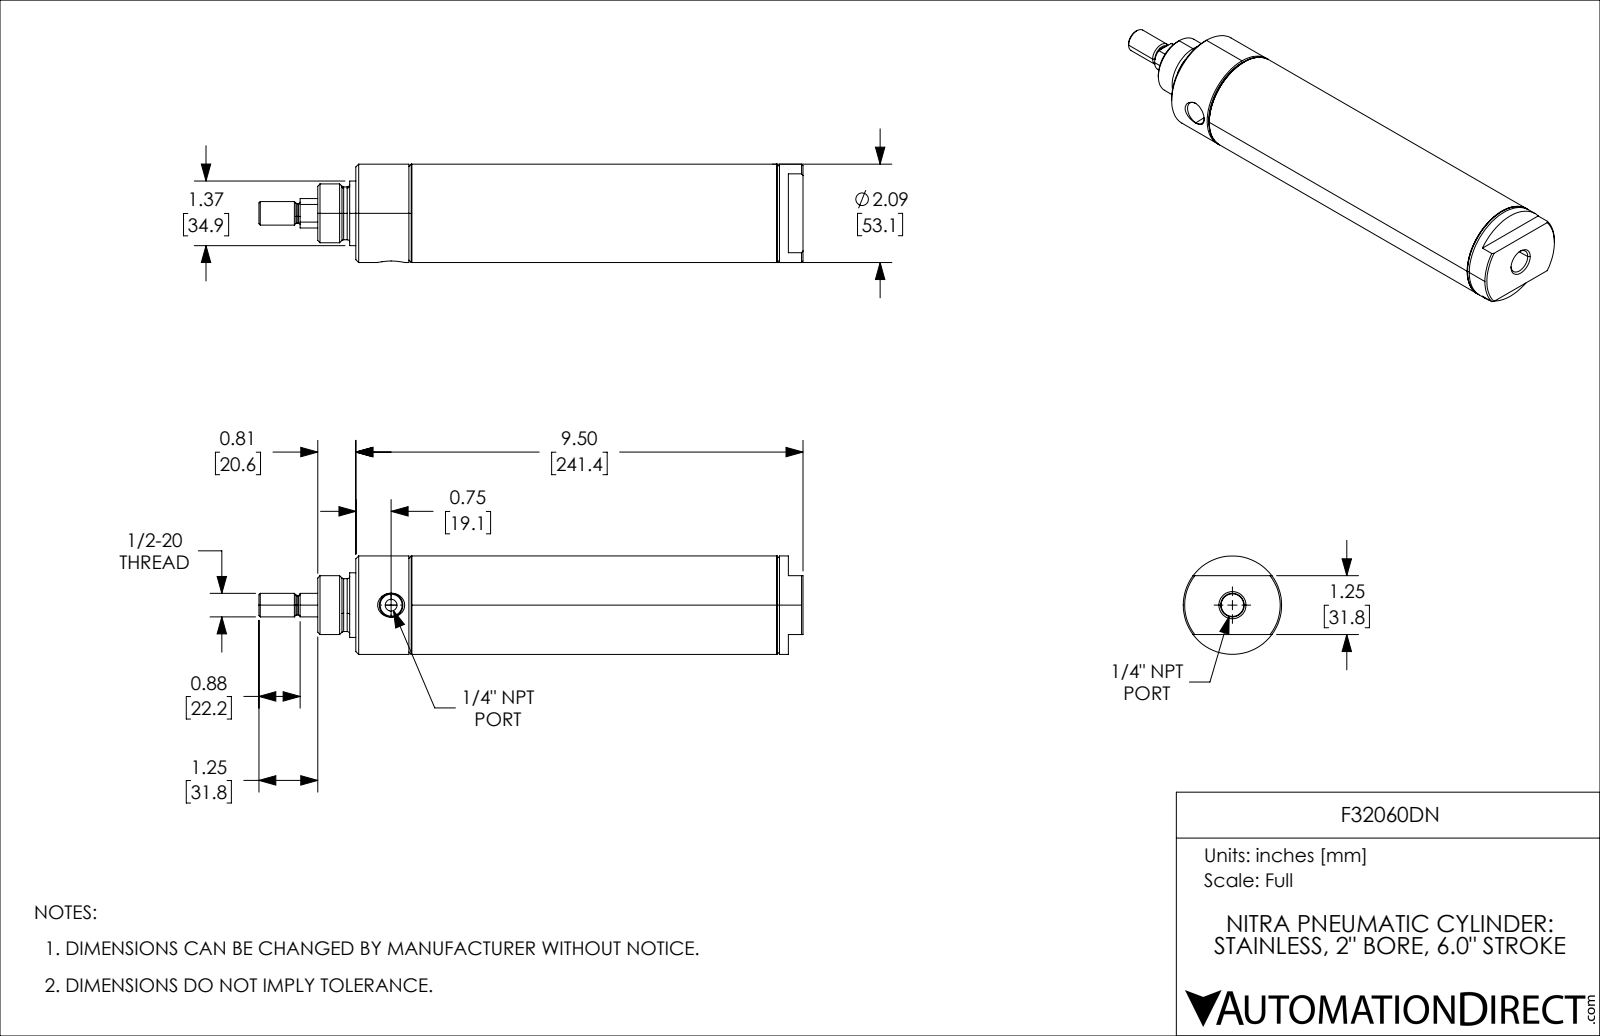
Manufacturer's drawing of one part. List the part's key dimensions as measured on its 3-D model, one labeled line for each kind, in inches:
Part name (STEP PRODUCT): F32060DN_3; F32060DN_7; F32060DN_5; F32060DN (+1 more)
STEP written by: SolidWorks 2021 (CONFIG_CONTROL_DESIGN)
Units: inches
Bodies: 4 solids, 133 faces (25 planar, 46 cylindrical, 62 other)
Overall size (bounding box): 11.562 × 2.09 × 2.09
Volume: 15.58 in³ · Surface area: 174.8 in²
Round holes (diameter × count): ⌀0.25 ×1, ⌀0.48 ×1, ⌀0.65 ×1, ⌀1.25 ×1, ⌀1.931 ×1
Round bosses / shafts (diameter × count): ⌀2.09 ×1, ⌀2.014 ×1, ⌀1.373 ×1, ⌀1.122 ×1, ⌀0.625 ×1, ⌀0.5 ×1, ⌀0.412 ×1
Main face-to-face distances: 1.188, 6, 7.188, 8, 2, 0.812, 1.502, 7.502, 8.69, 9.502
